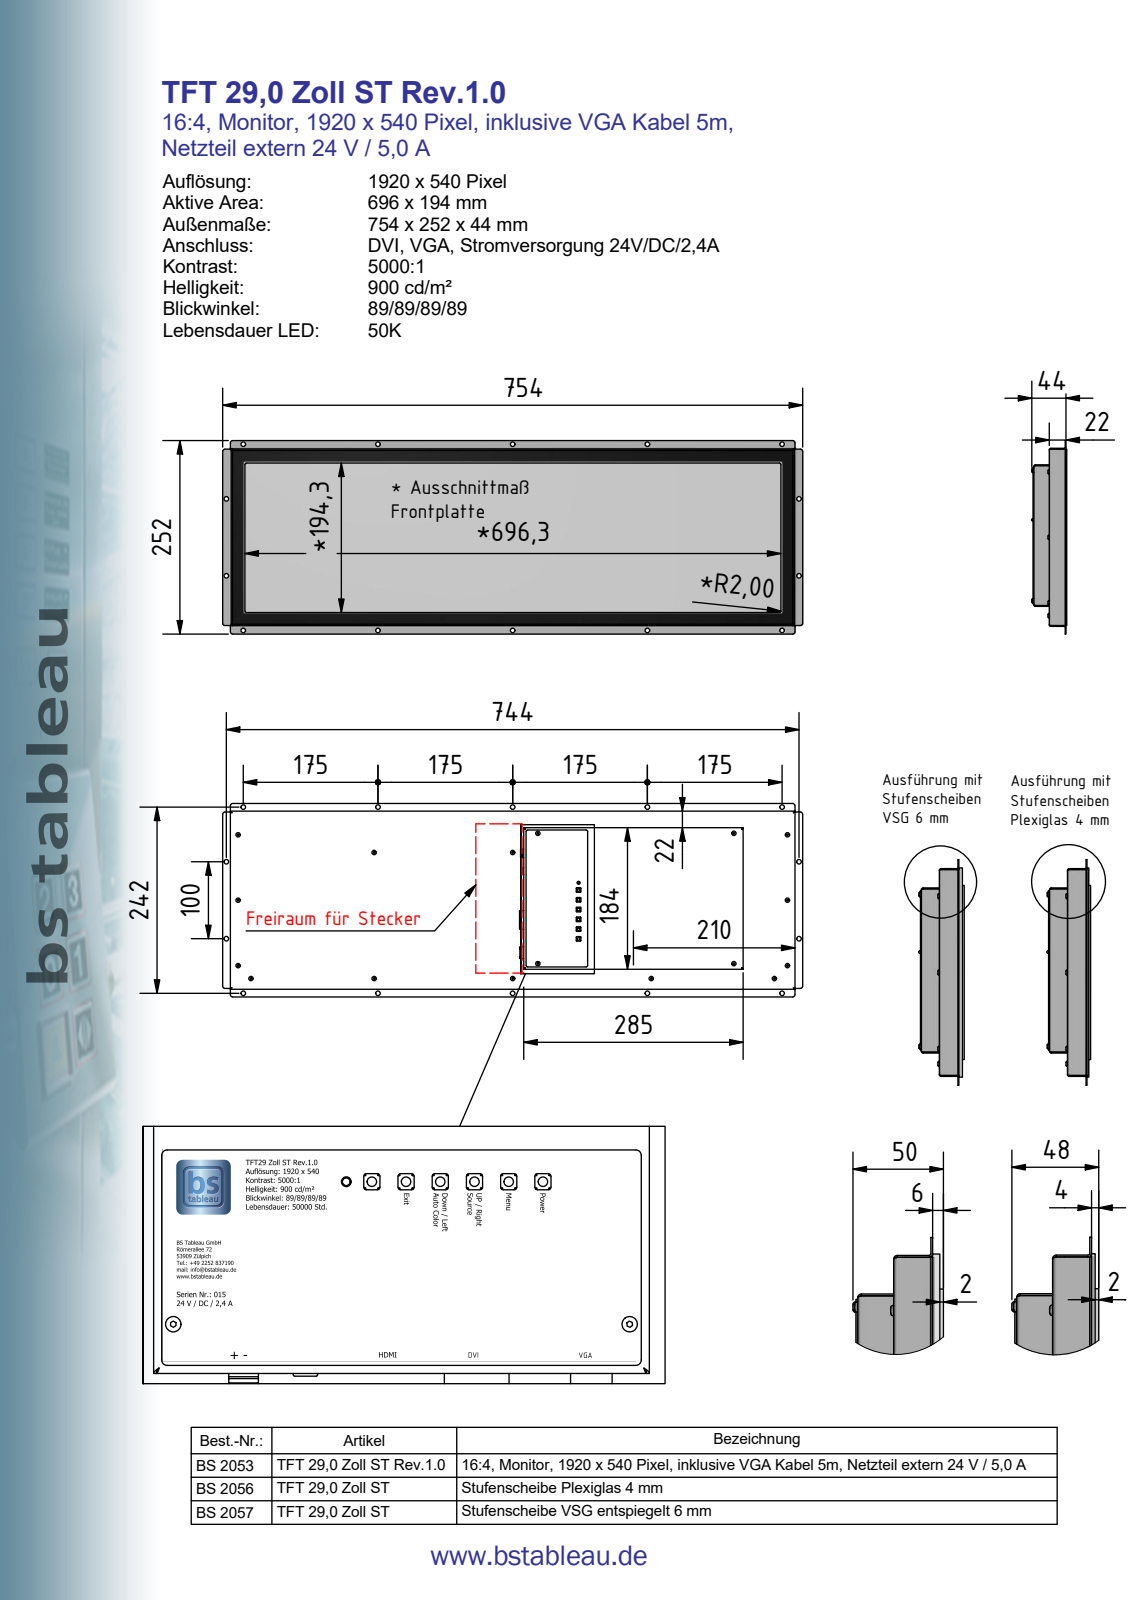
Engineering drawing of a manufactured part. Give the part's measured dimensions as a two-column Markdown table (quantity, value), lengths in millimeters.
| quantity | value |
| --- | --- |
| part name | 20000160 TFT 29,0 Zoll Strech Rev.1.0; 00003418 S290AJ1-LE1-F2; 00003419 TFT 29,0 Zoll Strech Rev.1.0 UT THV65; 00003420 TFT 29,0 Zoll Strech Rev.1.0 OT THV65 (+8 more) |
| STEP written by | Autodesk Inventor 2019 (AUTOMOTIVE_DESIGN) |
| units | millimeters |
| bodies | 48 solids, 4823 faces (3243 planar, 1096 cylindrical, 484 other) |
| overall size | 753.5 × 251.5 × 45.7 |
| volume | 3 165 000 mm³ |
| surface area | 992 748 mm² |
| round holes (diameter × count) | 3.2 × 23, 2.46 × 22, 1 × 15, 6 × 15, 5.41 × 11, 1.27 × 2, 2.26 × 2, 2.5 × 2, 2.54 × 2, 3.17 × 2, 3.3 × 2, 3.4 × 2 |
| round bosses / shafts (diameter × count) | 3 × 24, 0.5 × 24, 5.7 × 23, 5.42 × 9, 3.5 × 6, 3.56 × 2, 1 × 2, 2.9 × 1 |
| partial cylindrical surfaces (radius × count) | 0.1 × 174, 0.13 × 82, 2 × 46, 1 × 44, 0.25 × 41, 0.5 × 32, 0.51 × 17, 1.02 × 13 |
| main face-to-face distances | 1, 20.7, 21.7, 5.5, 6.5, 15.2, 20, 21, 41.7, 40.7 |
| hole center spacings | 2.26, 3.95, 2.29, 4.58, 4.52, 6.02, 6.04, 6.87 |
